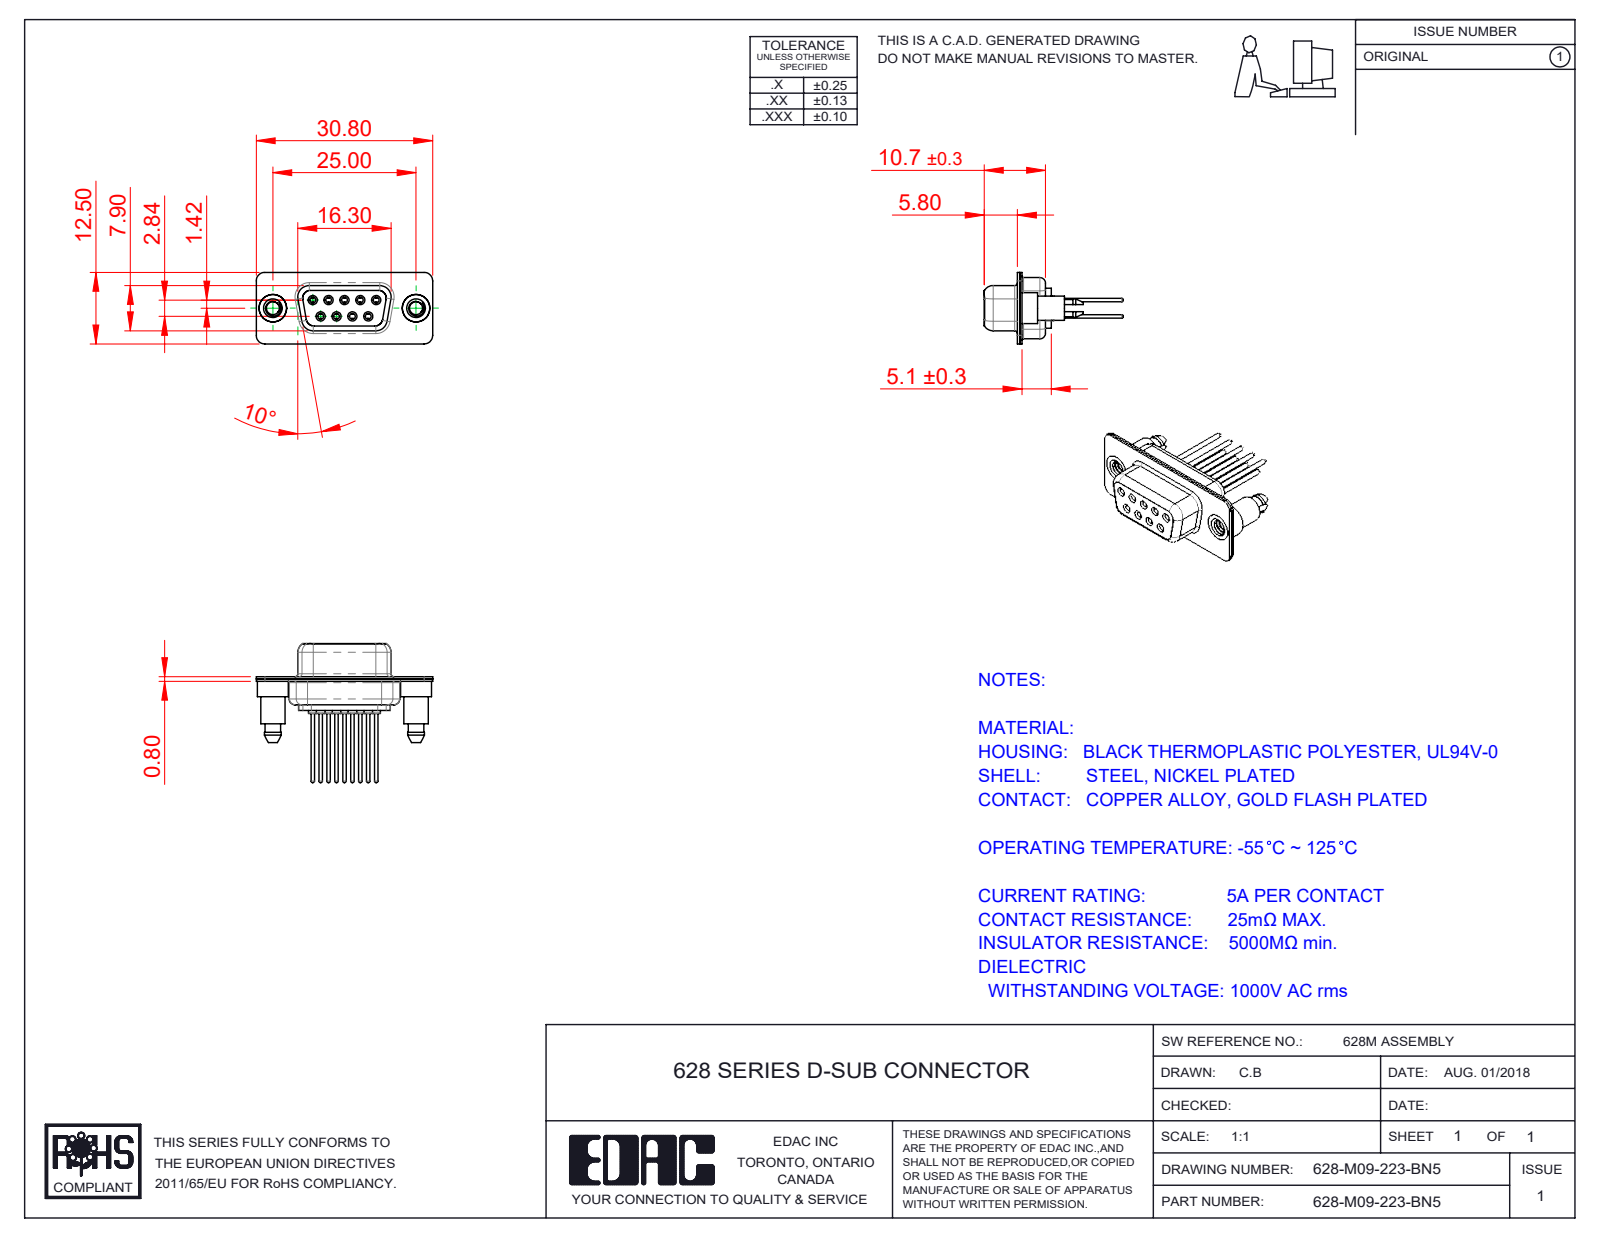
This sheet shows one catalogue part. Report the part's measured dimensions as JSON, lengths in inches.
{"part_name": "628M 4-40 Threaded Boardlock; 628M Contact Row 2_23; 628-M09-223-BN5; 628M Housing_09 Contacts (+3 more)", "step_written_by": "SolidWorks 2020 (CONFIG_CONTROL_DESIGN)", "units": "inches", "bodies": {"solids": 14, "faces": 824, "planar": 218, "cylindrical": 340, "other": 266}, "overall_size": [1.213, 0.956, 0.492], "volume_in3": 0.113, "surface_area_in2": 7.547, "round_holes": [[0.039, 9], [0.043, 9], [0.067, 9], [0.071, 9], [0.079, 9], [0.089, 2], [0.157, 2], [0.189, 2]], "round_bosses_or_shafts": [[0.087, 9], [0.063, 9], [0.059, 9], [0.024, 9], [0.213, 2], [0.193, 2], [0.167, 2]], "partial_cylinders_radius": [[0.059, 18], [0.079, 12], [0.063, 10], [0.053, 8], [0.01, 4], [0.02, 4], [0.024, 4], [0.026, 4]], "face_to_face_distances": [0.016, 0.055, 0.018, 0.333, 0.031, 0.071, 0.039, 0.35, 0.244, 0.278], "hole_center_spacings": [0.124, 0.109, 0.218, 0.198, 0.198, 0.327, 0.28, 0.294]}
